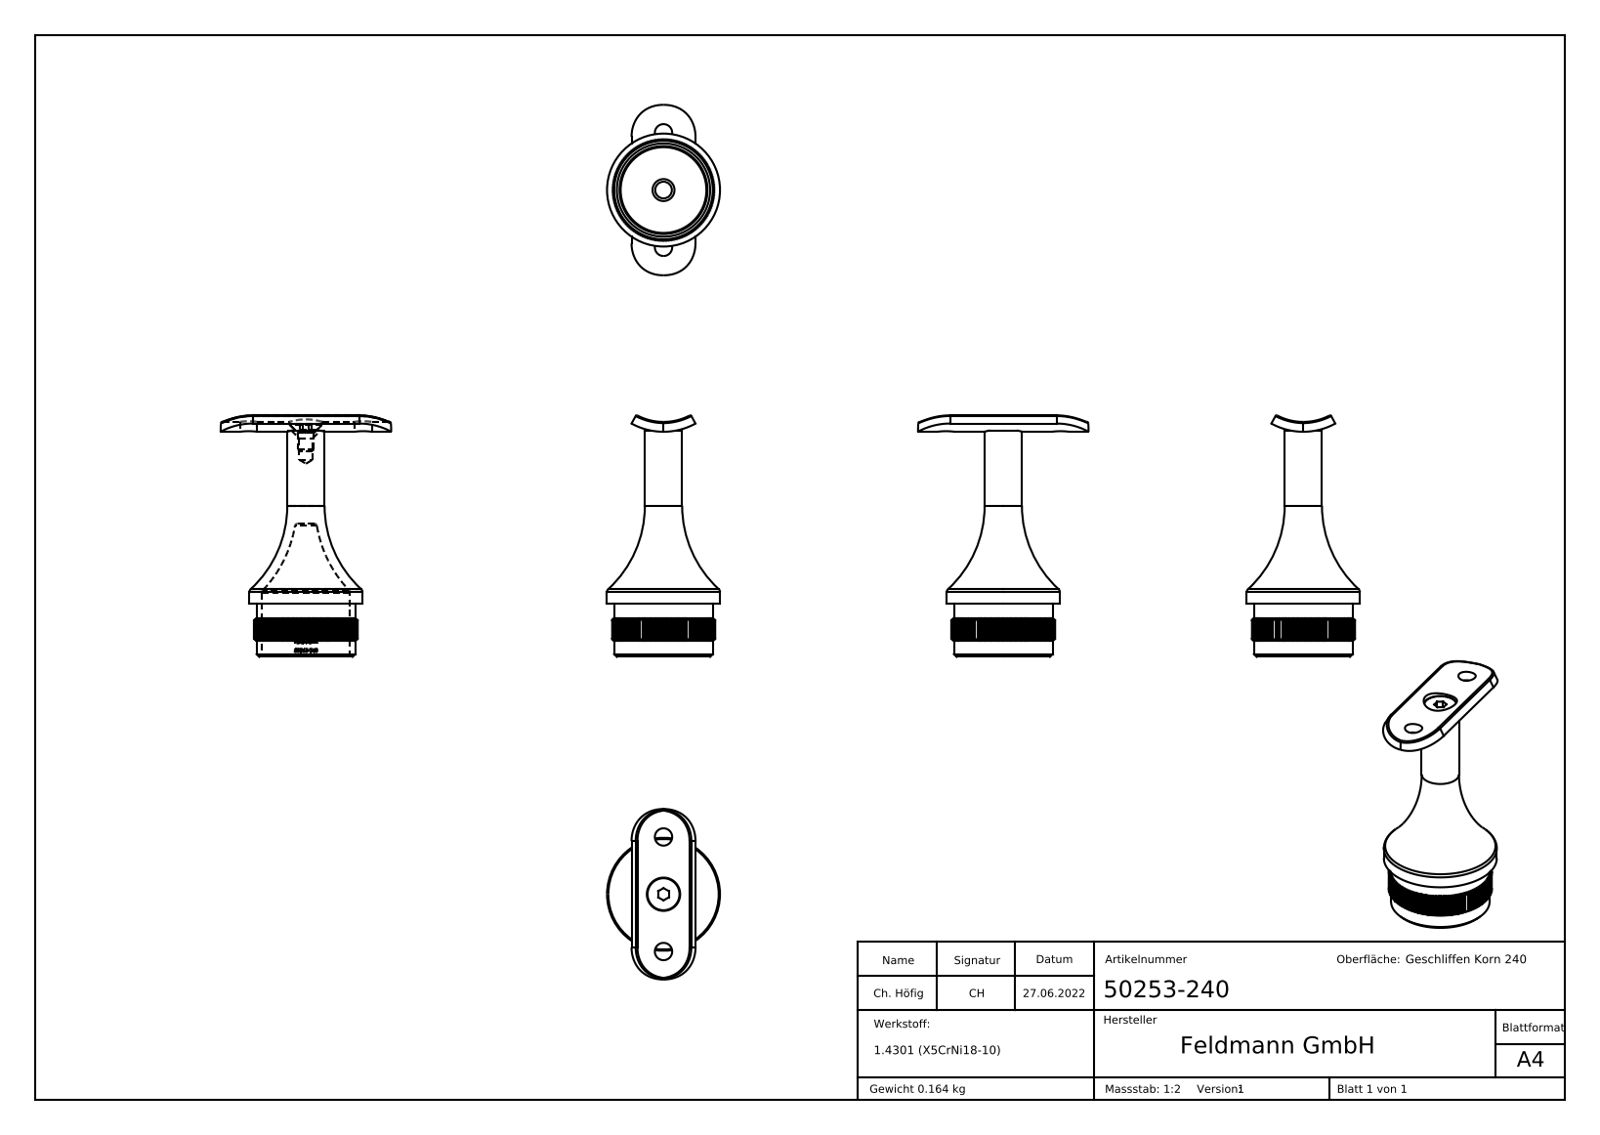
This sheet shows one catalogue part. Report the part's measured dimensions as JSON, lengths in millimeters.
{"part_name": "DIN 7991 Konfig_DIN 7991 M6x10; 50253-240; 5025x-240 Teil1_50253-240 Teil1; 5025x-240 Teil2_5025x-240 Teil2", "step_written_by": "SolidWorks 2018 (CONFIG_CONTROL_DESIGN)", "units": "millimeters", "bodies": {"solids": 3, "faces": 929, "planar": 375, "cylindrical": 170, "other": 384}, "overall_size": [90.65, 64, 42.4], "volume_mm3": 24265, "surface_area_mm2": 16552, "round_holes": [[6.5, 2], [5, 1], [8.1, 1], [12.5, 1], [33, 1]], "round_bosses_or_shafts": [[42.4, 1], [37, 1], [14, 1], [12, 1], [6, 1]], "partial_cylinders_radius": [[12, 4], [0.5, 2], [7.1, 1], [16.6, 1], [19.32, 1], [21.2, 1], [24.9, 1]], "face_to_face_distances": [18.5, 18.49, 18.48, 18.52, 18.51, 65, 20, 85, 87.35, 67.35], "hole_center_spacings": [21.5, 43]}
